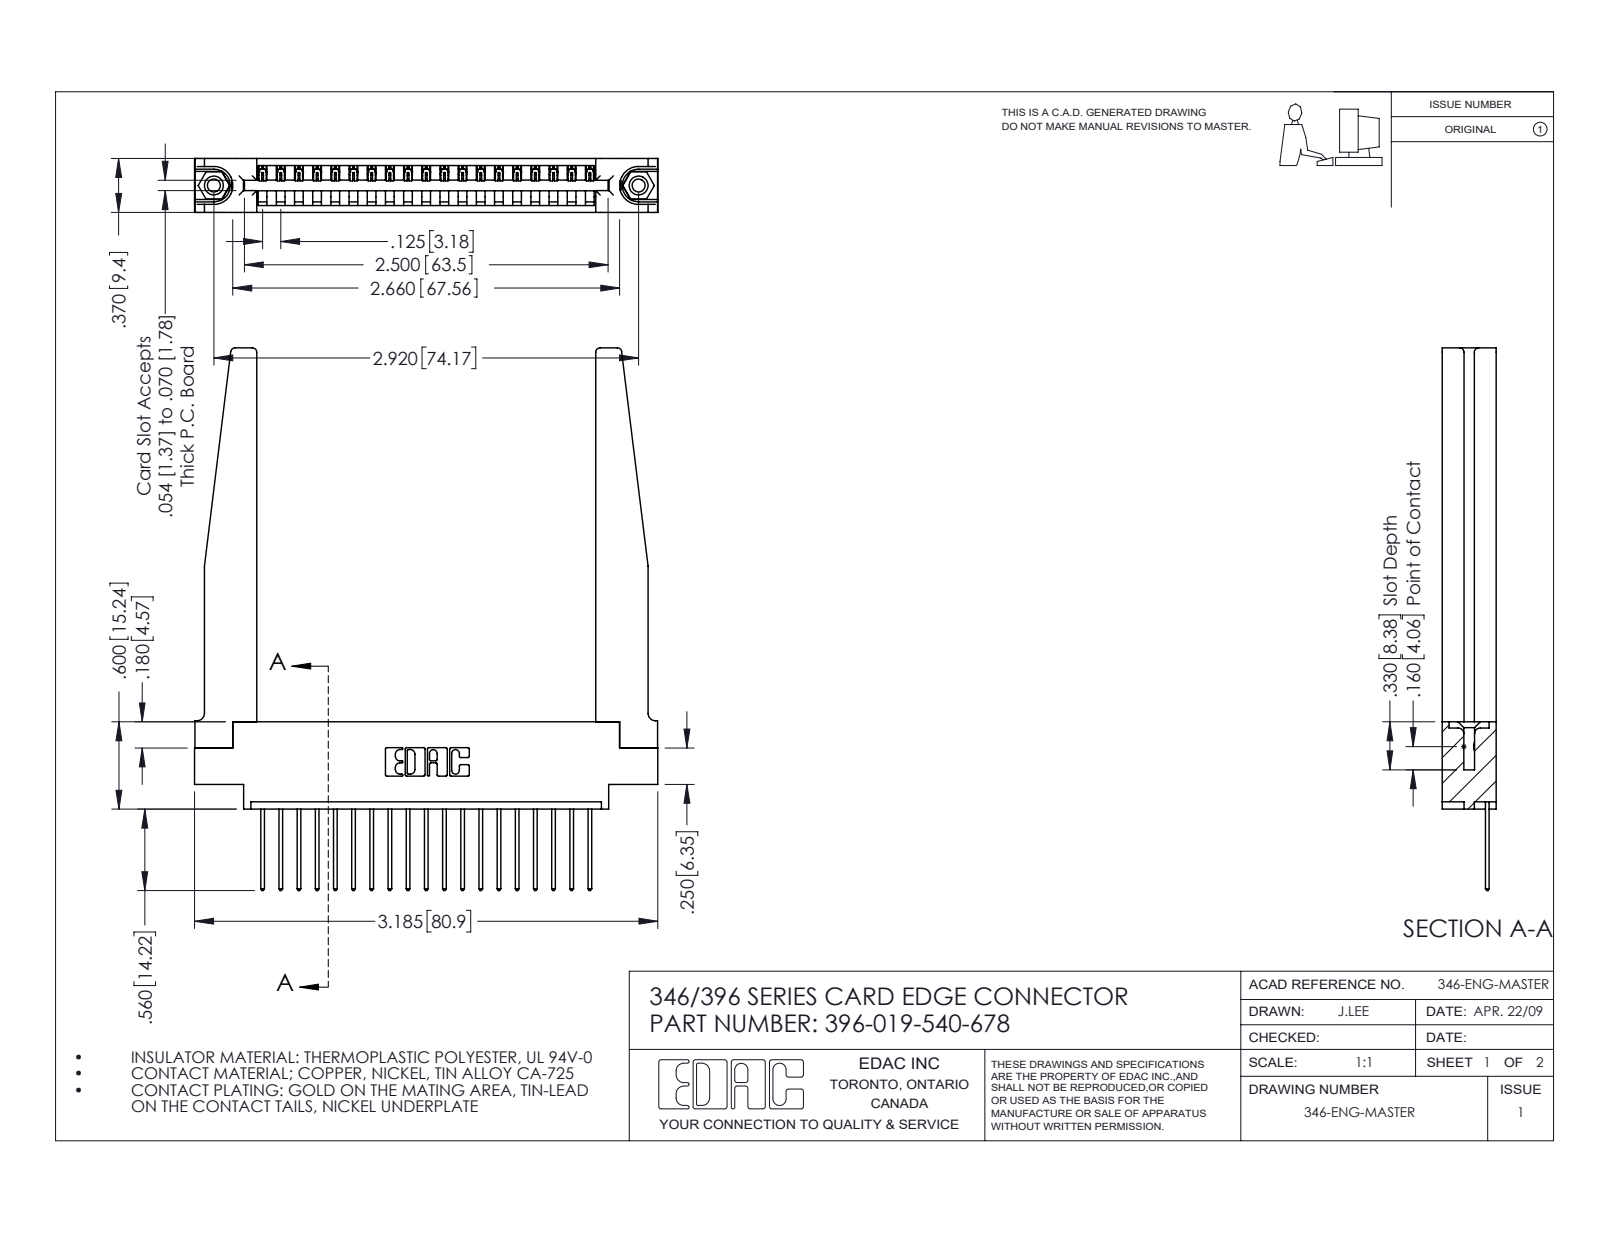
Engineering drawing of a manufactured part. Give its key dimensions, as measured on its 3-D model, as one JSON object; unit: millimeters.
{"part_name": "345-250-001_345-250-001-102; 396-019-540-678; 346-220-078_345-220-078; 345-292-001_345-293-140 (+1 more)", "step_written_by": "SolidWorks 2016 (CONFIG_CONTROL_DESIGN)", "units": "millimeters", "bodies": {"solids": 24, "faces": 1462, "planar": 982, "cylindrical": 428, "other": 52}, "overall_size": [94.7, 80.9, 9.4], "volume_mm3": 14400, "surface_area_mm2": 15960, "round_holes": [[2.3, 2], [3.2, 2], [4, 2], [1.6, 1]], "round_bosses_or_shafts": [[3.9, 2]], "partial_cylinders_radius": [[0.2, 38], [0.3, 38], [0.3, 22], [0.8, 8], [0.2, 6], [0.8, 6], [0.7, 3], [0.8, 2]], "face_to_face_distances": [9.4, 1.8, 1.2, 8.2, 3.8, 3.8, 6.4, 7.6, 0.6, 2.6], "hole_center_spacings": [6.2, 68.9, 74.2]}
